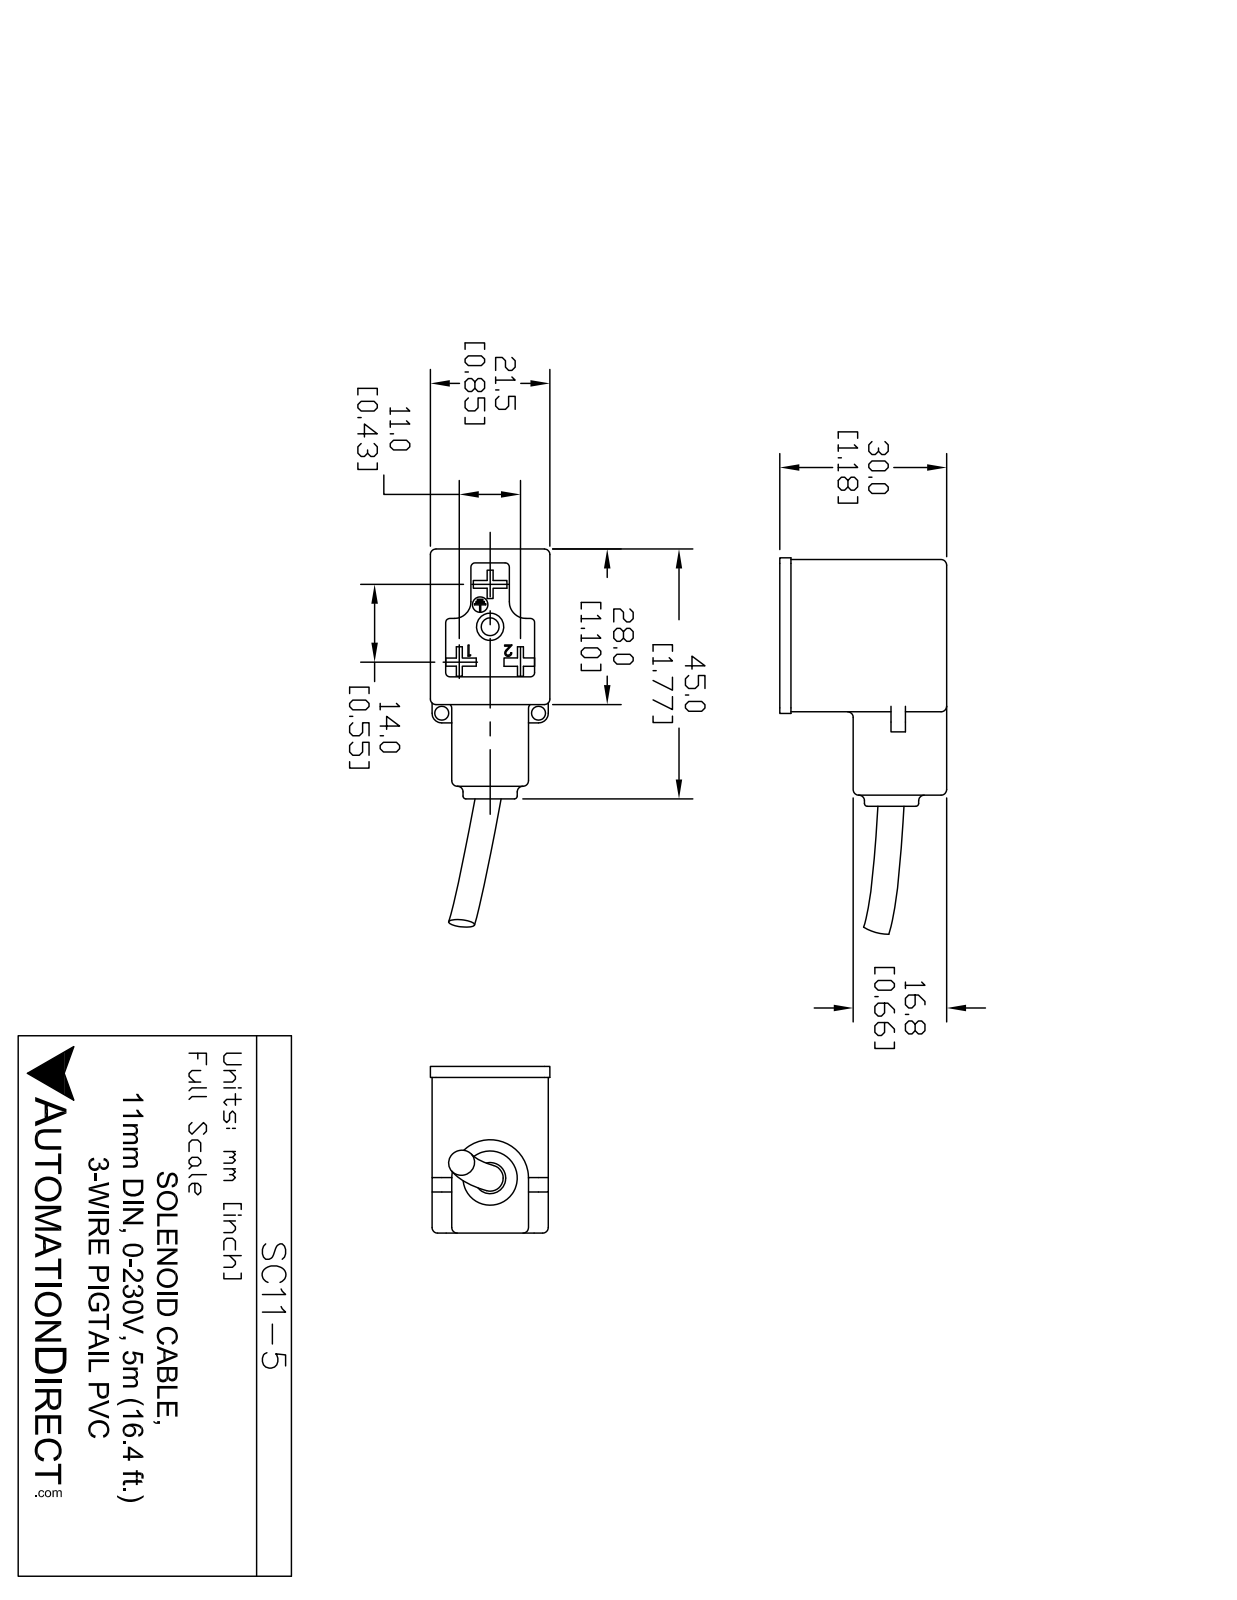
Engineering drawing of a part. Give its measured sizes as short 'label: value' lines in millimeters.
name: SC11-5
written by: SolidWorks 2011 (AUTOMOTIVE_DESIGN)
unit: mm
bodies: 3 solids, 197 faces (131 planar, 45 cylindrical, 21 other)
size: 67.77 × 34.3 × 21.5
volume: 19 925 mm³; area: 7 593 mm²
holes: 2× ⌀2.5, 1× ⌀2.78, 1× ⌀3.2, 1× ⌀4.9, 1× ⌀5.6, 1× ⌀6.6
bosses: 1× ⌀9.75, 1× ⌀6.5, 1× ⌀2.75
rounds: 21× R0.75, 6× R1, 2× R1.75, 2× R3, 1× R6.9
face distances: 20.9, 2, 28, 30, 27.4, 3.55, 17.35, 7, 9.45, 27.95
hole spacings: 17.82, 21.65, 4.27, 17.4
